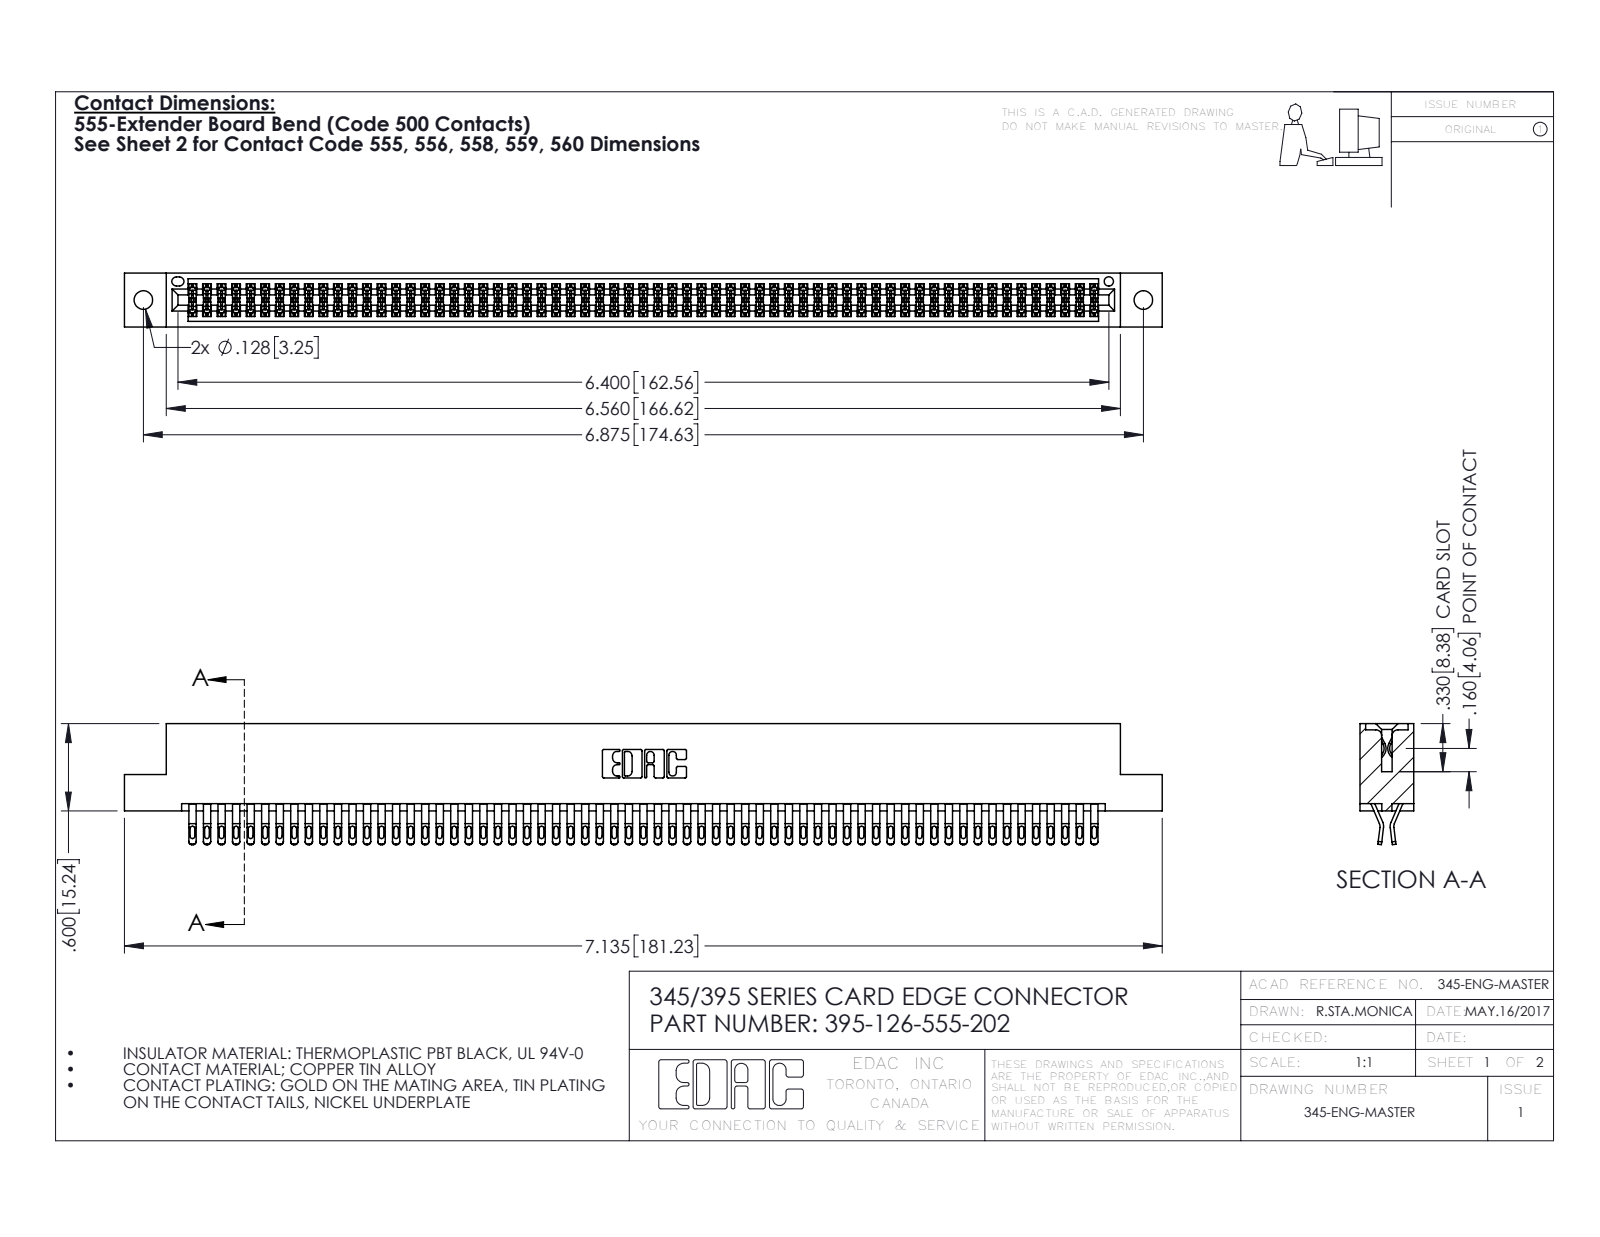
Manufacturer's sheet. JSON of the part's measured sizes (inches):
{"part_name": "345-292-001_555 Tail; 395-126-555-202; 345 Part_Flush Mounting Lugs - 0.128 Dia", "step_written_by": "SolidWorks 2016 (CONFIG_CONTROL_DESIGN)", "units": "inches", "bodies": {"solids": 127, "faces": 7182, "planar": 3986, "cylindrical": 3196, "other": 0}, "overall_size": [7.135, 0.832, 0.37], "volume_in3": 1.106, "surface_area_in2": 43.71, "round_holes": [[0.128, 2], [0.064, 1]], "partial_cylinders_radius": [[0.016, 315], [0.02, 252], [0.006, 189], [0.01, 22], [0.007, 6], [0.031, 6], [0.026, 3], [0.01, 2]], "face_to_face_distances": [0.298, 0.072, 0.025, 0.37, 0.2, 0.098, 0.272, 0.225, 0.175, 0.149], "hole_center_spacings": [0.27, 6.639, 6.875]}
